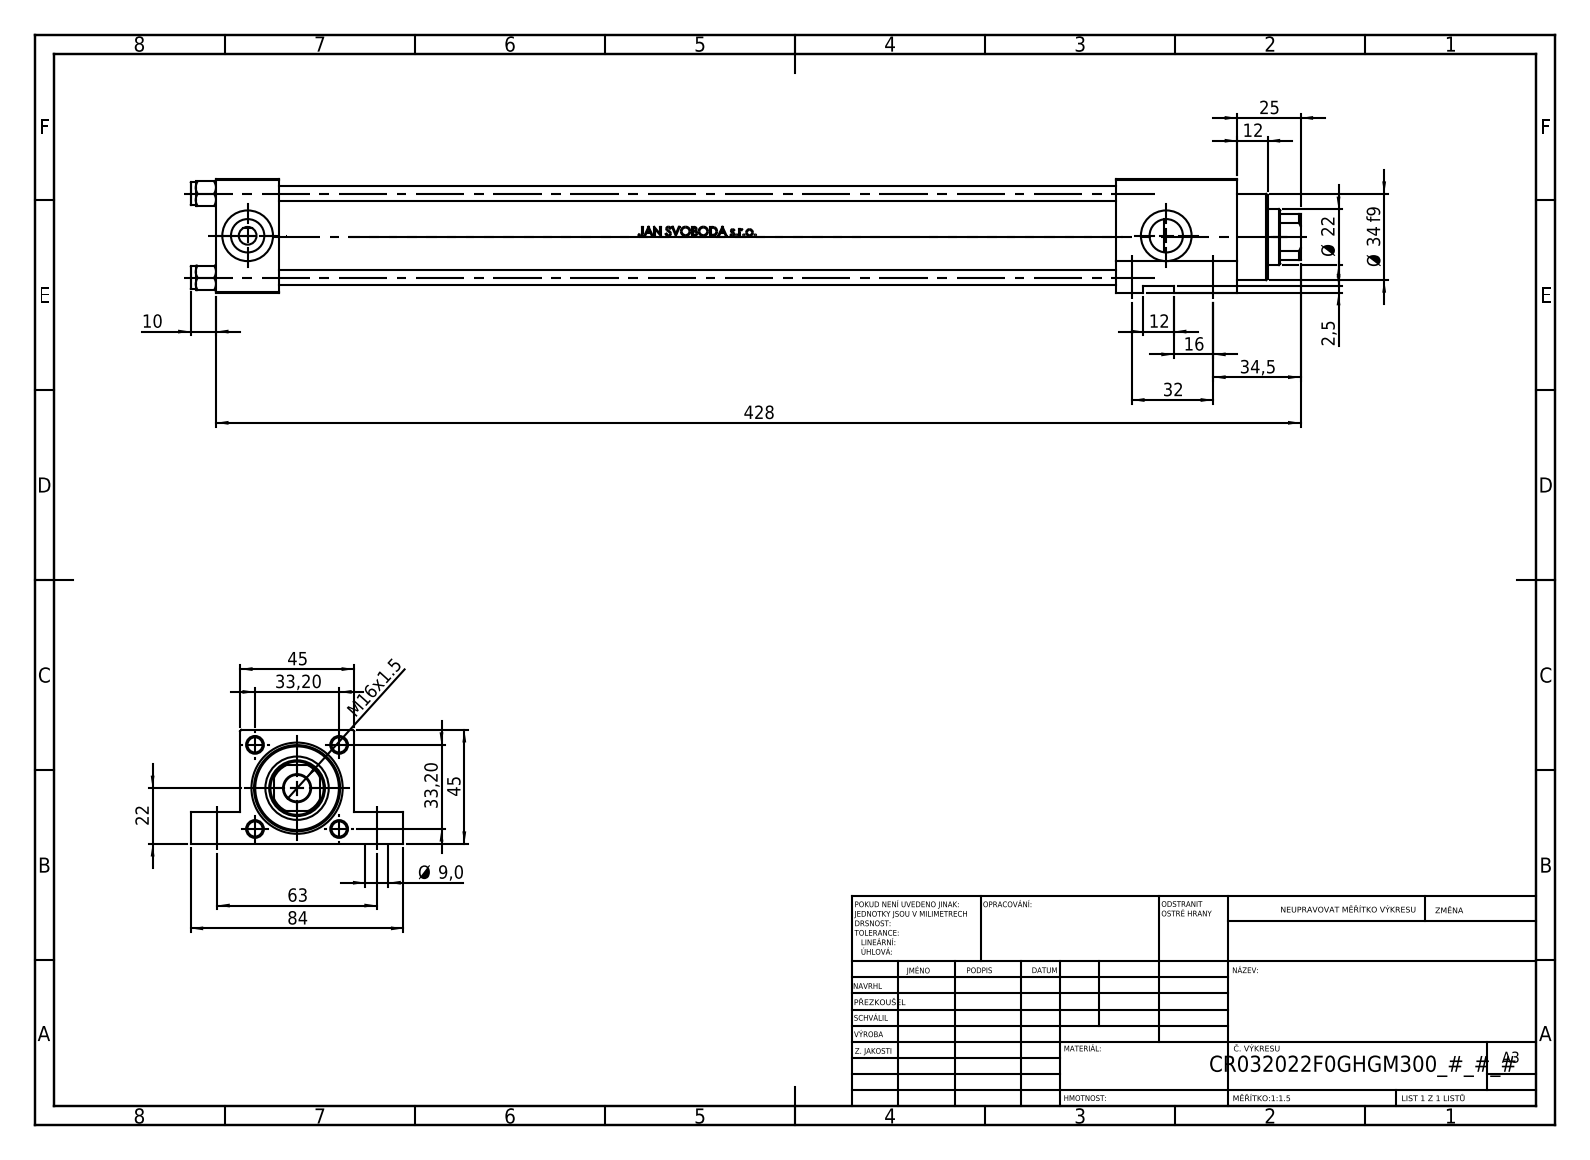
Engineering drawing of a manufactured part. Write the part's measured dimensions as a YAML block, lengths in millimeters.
part_name: "V215CR_F_Body; V215CR_VCP_F; V215CR_F_TYCINKA; V215_VC_A (+1 more)"
step_written_by: "SolidWorks 2019 (CONFIG_CONTROL_DESIGN)"
units: millimeters
bodies: {solids: 11, faces: 1102, planar: 436, cylindrical: 126, other: 540}
overall_size: [438, 84, 45]
volume: 458676
surface_area: 178841
round_holes:
  - {diameter: 6, count: 4}
  - {diameter: 9, count: 4}
  - {diameter: 7, count: 2}
  - {diameter: 13.16, count: 2}
  - {diameter: 20, count: 2}
  - {diameter: 10.5, count: 1}
  - {diameter: 22, count: 1}
  - {diameter: 24, count: 1}
  - {diameter: 25, count: 1}
  - {diameter: 32, count: 1}
  - {diameter: 33, count: 1}
round_bosses_or_shafts:
  - {diameter: 9, count: 4}
  - {diameter: 38, count: 1}
  - {diameter: 34, count: 1}
partial_cylinders:
  - {radius: 10.5, count: 1}
face_to_face_distances: [45, 25, 378, 403, 355, 330, 12.5, 32.5, 48, 10]
hole_center_spacings: [33.2, 23.13, 23.83, 32, 46.95, 63, 70.66, 362.5]
